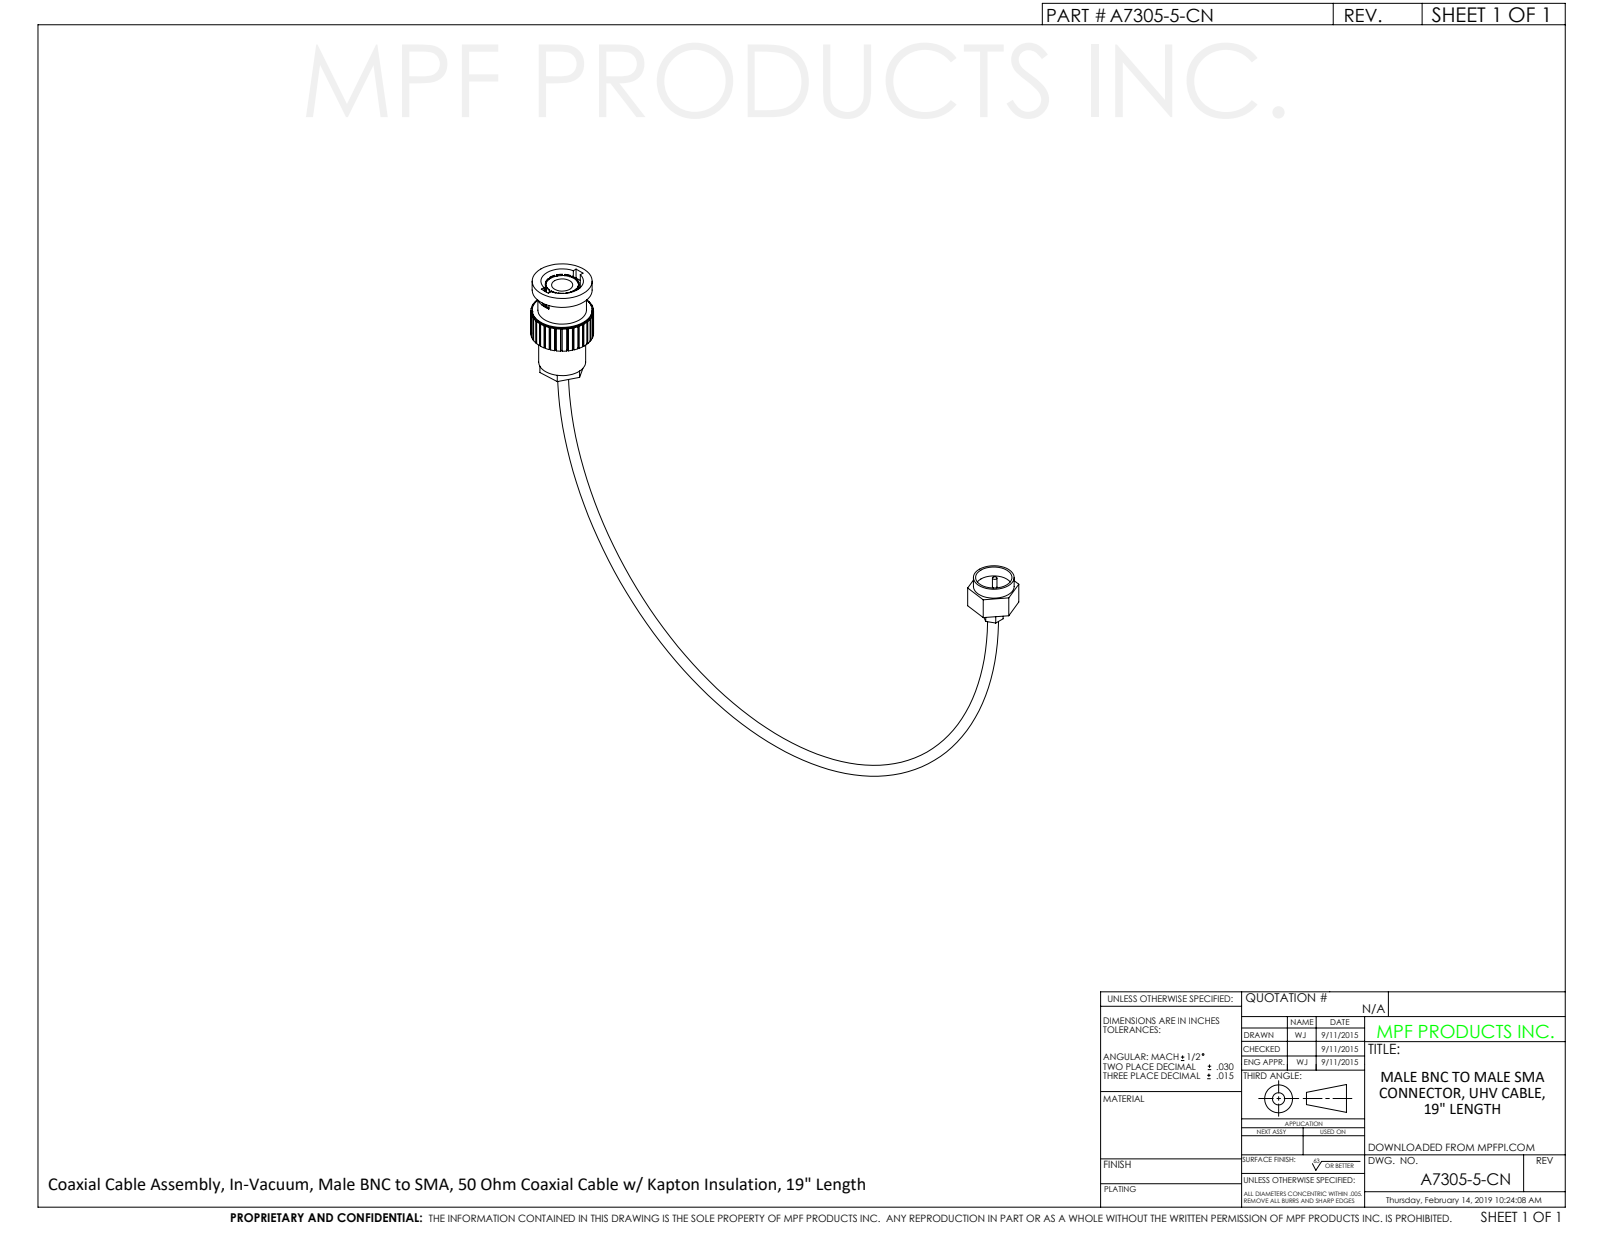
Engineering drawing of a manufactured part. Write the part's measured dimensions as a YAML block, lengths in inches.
part_name: "A7305-5-CN"
step_written_by: "SolidWorks 2012 (CONFIG_CONTROL_DESIGN)"
units: inches
bodies: {solids: 2, faces: 331, planar: 237, cylindrical: 92, other: 2}
overall_size: [6.109, 3.816, 0.575]
volume: 0.239
surface_area: 7.38
round_holes:
  - {diameter: 0.074, count: 1}
  - {diameter: 0.158, count: 1}
  - {diameter: 0.194, count: 1}
  - {diameter: 0.334, count: 1}
  - {diameter: 0.39, count: 1}
round_bosses_or_shafts:
  - {diameter: 0.55, count: 1}
  - {diameter: 0.525, count: 1}
  - {diameter: 0.445, count: 1}
  - {diameter: 0.43, count: 1}
  - {diameter: 0.374, count: 1}
  - {diameter: 0.308, count: 1}
  - {diameter: 0.041, count: 1}
partial_cylinders:
  - {radius: 0.068, count: 1}
  - {radius: 0.15, count: 1}
  - {radius: 0.151, count: 1}
  - {radius: 0.287, count: 1}
face_to_face_distances: [0.409, 0.15, 0.35, 0.2, 0.978, 0.828, 0.628, 0.1, 0.528, 0.54]
hole_center_spacings: [5.595]
